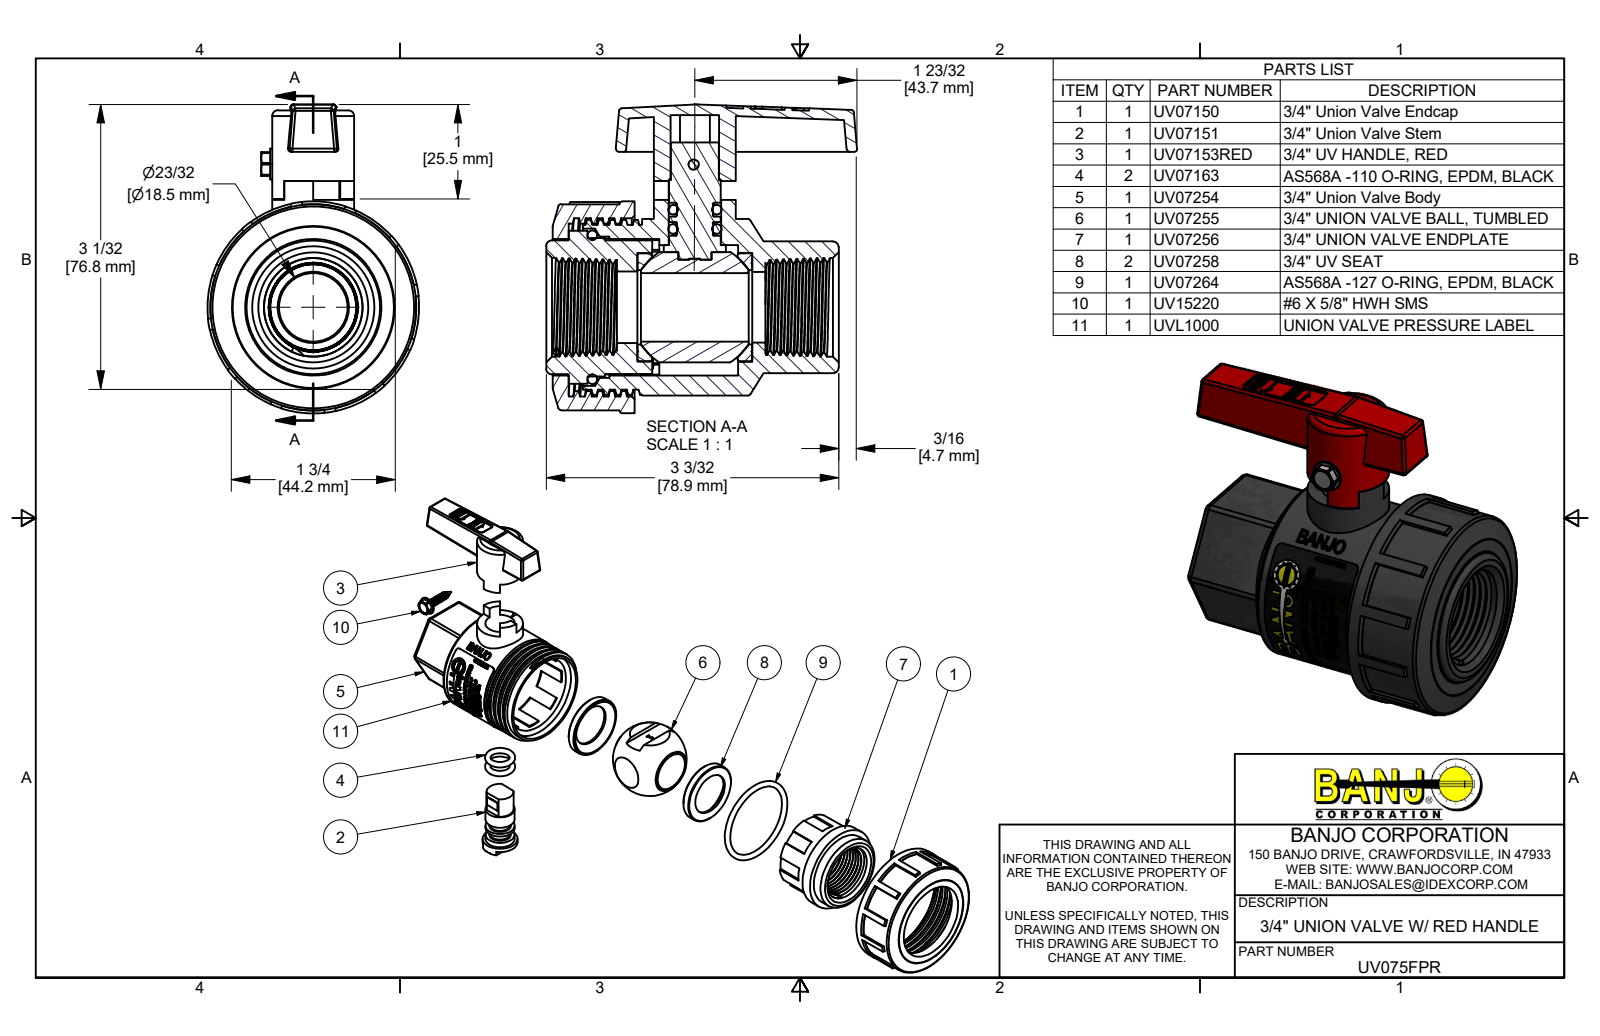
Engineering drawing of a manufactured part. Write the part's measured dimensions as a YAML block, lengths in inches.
part_name: "UV075FPR; UV07254; UVL1000-D1.875; UV07256 (+8 more)"
step_written_by: "Autodesk Inventor 2019 (AUTOMOTIVE_DESIGN)"
units: inches
bodies: {solids: 13, faces: 2337, planar: 1190, cylindrical: 364, other: 783}
overall_size: [30.797, 3.279, 2.25]
volume: 6.784
surface_area: 252.5
round_holes:
  - {diameter: 0.515, count: 1}
  - {diameter: 0.558, count: 1}
  - {diameter: 0.727, count: 1}
  - {diameter: 0.75, count: 1}
  - {diameter: 0.76, count: 1}
  - {diameter: 0.79, count: 1}
  - {diameter: 1.153, count: 1}
  - {diameter: 1.157, count: 1}
  - {diameter: 1.45, count: 1}
  - {diameter: 1.5, count: 1}
  - {diameter: 1.67, count: 1}
  - {diameter: 1.778, count: 1}
round_bosses_or_shafts:
  - {diameter: 2.25, count: 1}
  - {diameter: 2.187, count: 1}
  - {diameter: 1.875, count: 1}
  - {diameter: 1.856, count: 1}
  - {diameter: 1.75, count: 1}
  - {diameter: 1.625, count: 1}
  - {diameter: 1.47, count: 1}
  - {diameter: 1.42, count: 1}
partial_cylinders:
  - {radius: 0.03, count: 22}
  - {radius: 0.06, count: 16}
  - {radius: 0.01, count: 4}
  - {radius: 0.05, count: 4}
  - {radius: 0.5, count: 3}
  - {radius: 0.139, count: 1}
  - {radius: 0.255, count: 1}
  - {radius: 0.287, count: 1}
face_to_face_distances: [1.4, 0.731, 1.955, 1.224, 0.7, 0.11, 1.255, 0.031, 0.2, 0.115]
